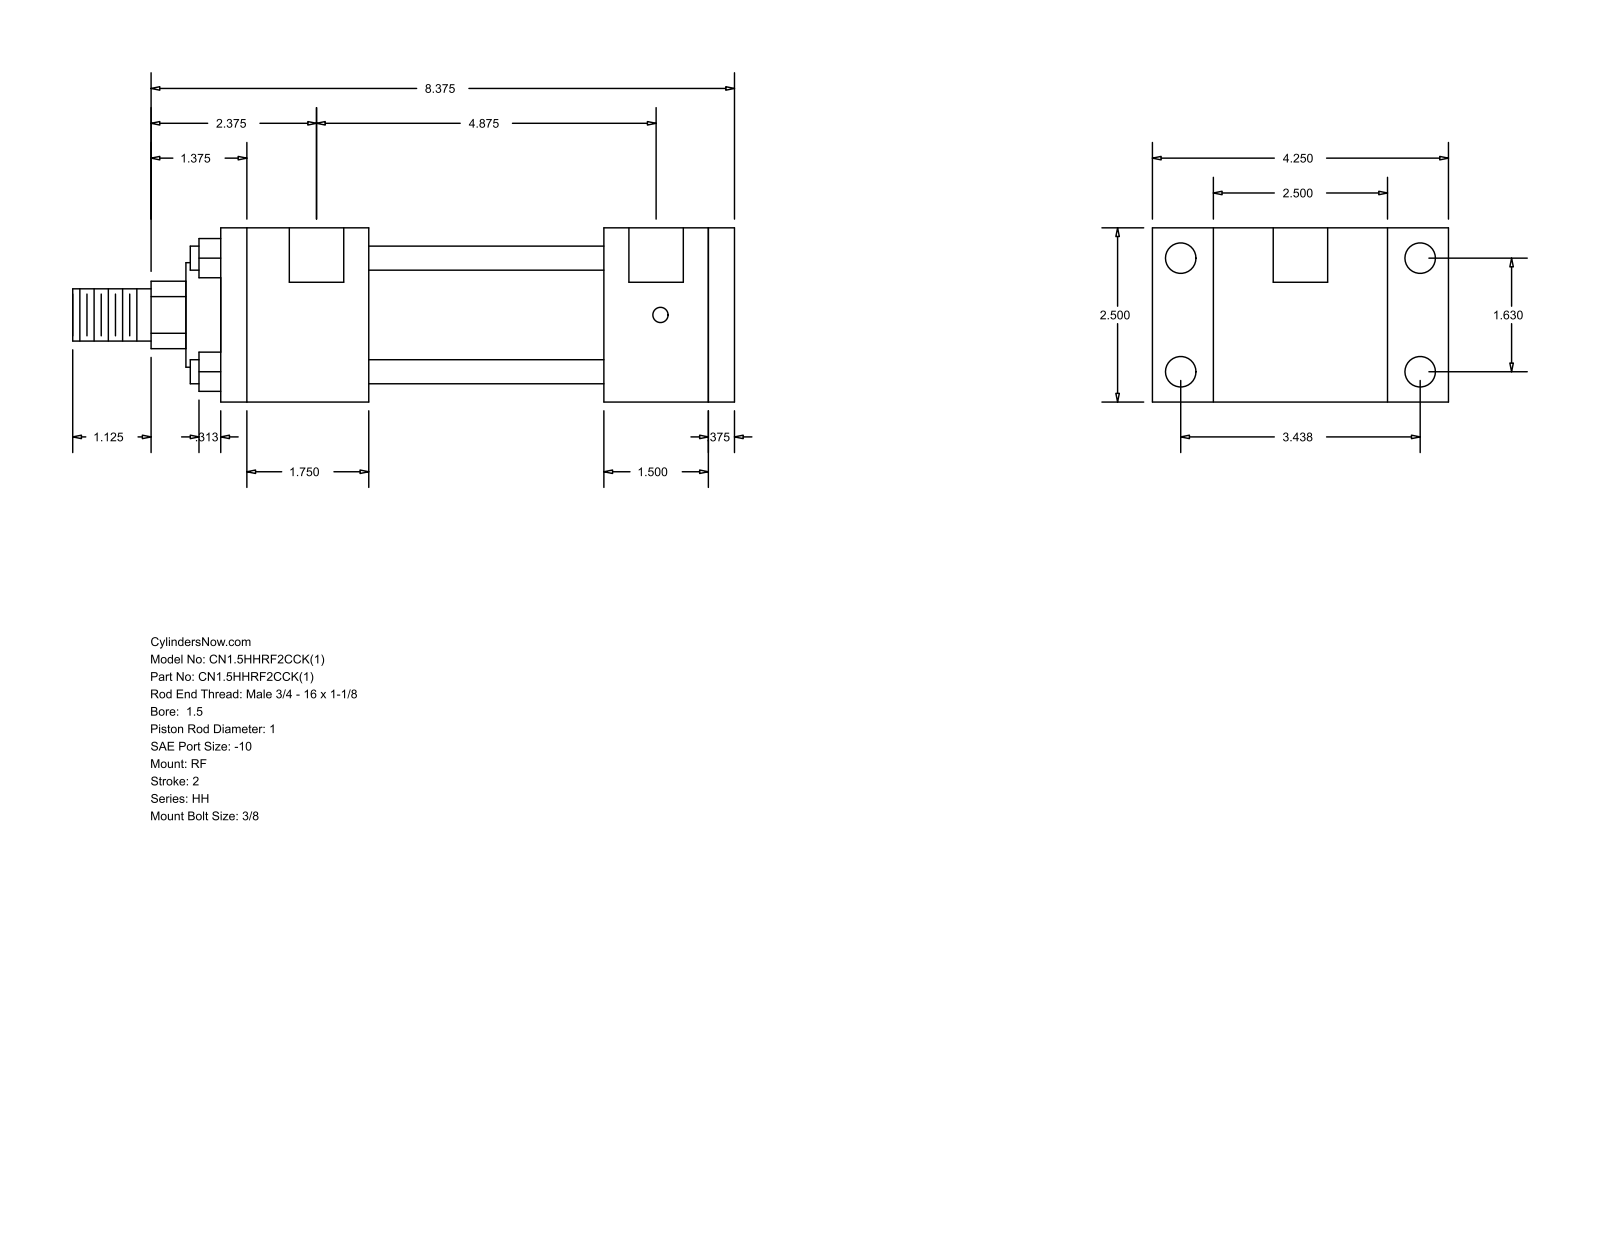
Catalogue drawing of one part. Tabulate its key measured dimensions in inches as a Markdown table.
| quantity | value |
| --- | --- |
| part name | HH_RF__0150_1 |
| STEP written by | GSSL Pune (CONFIG_CONTROL_DESIGN) |
| units | inches |
| bodies | 0 solids, 92 faces (64 planar, 28 cylindrical, 0 other) |
| overall size | 9.5 × 4.25 × 2.5 |
| round holes (diameter × count) | 0.219 × 4, 0.438 × 4, 0.781 × 2 |
| round bosses / shafts (diameter × count) | 0.345 × 4, 1.75 × 1, 1.5 × 1, 1 × 1, 0.75 × 1 |
| partial cylindrical surfaces (radius × count) | 0.484 × 1 |
| main face-to-face distances | 2.5, 0.375, 1.5, 3.375, 4.875, 5.25, 1.875, 2.125, 5.5, 7 |
| hole center spacings | 0.063, 1.63, 3.438, 3.805, 4.937, 5, 4.875 |
